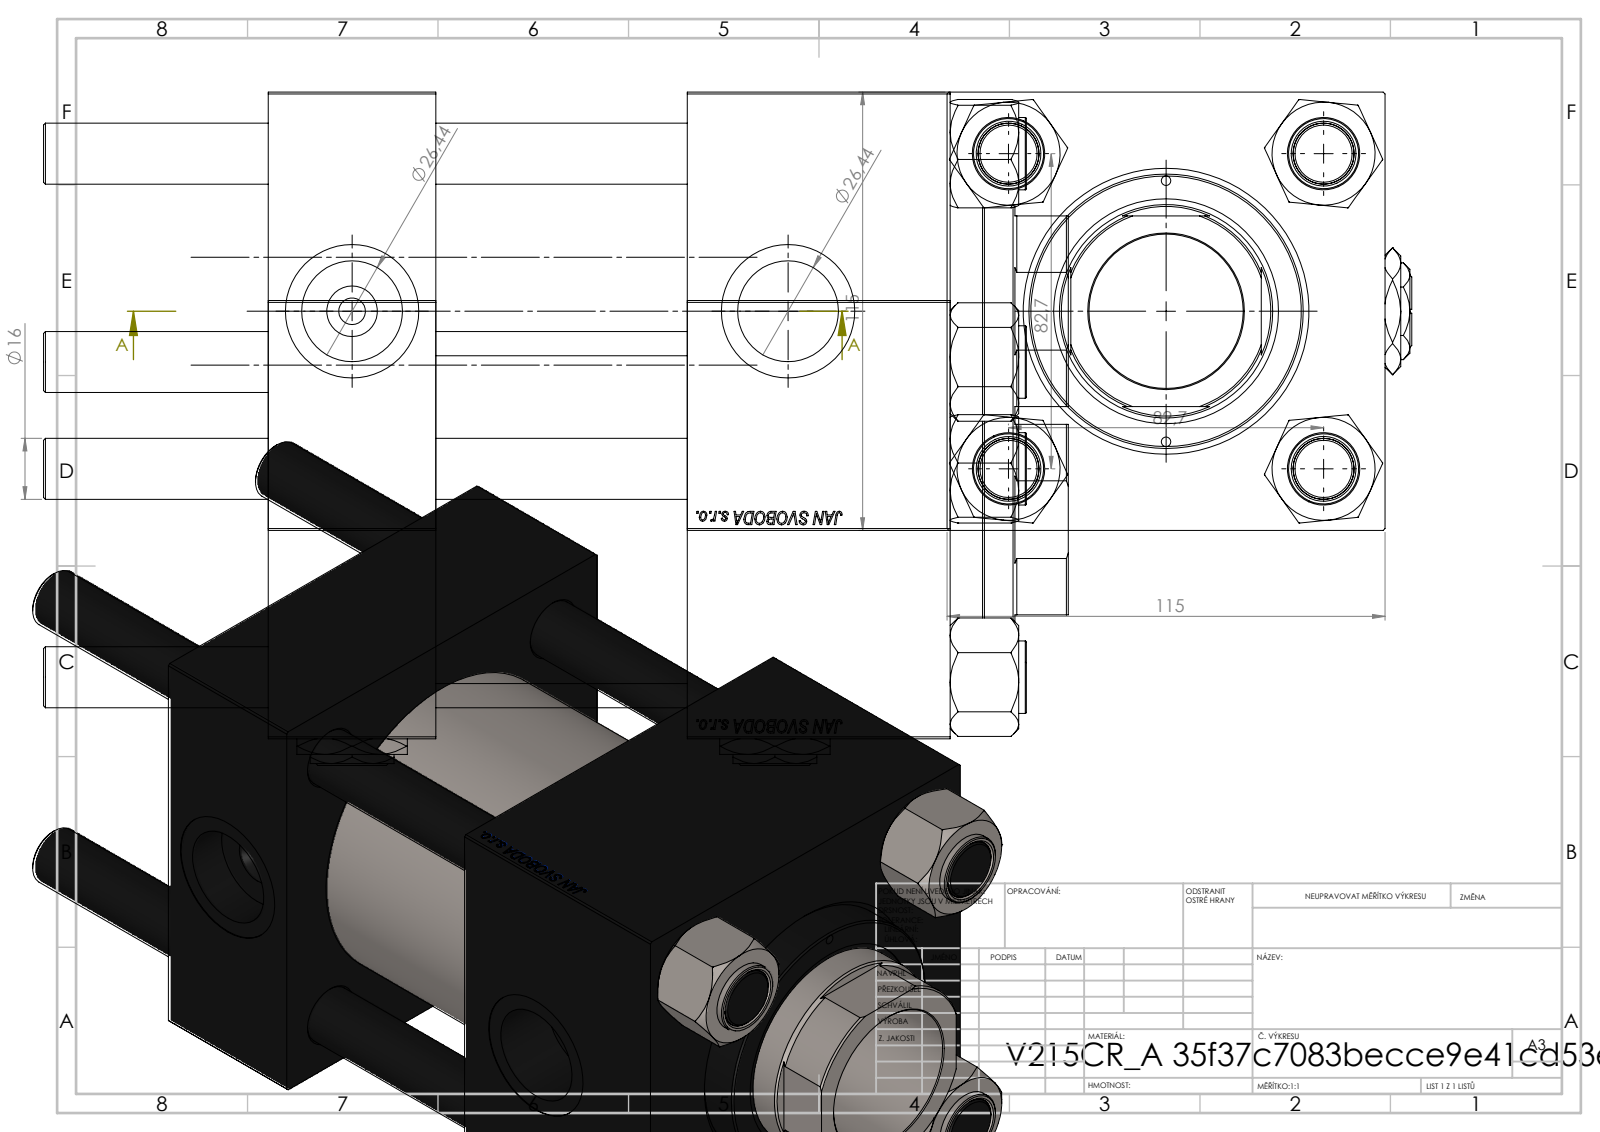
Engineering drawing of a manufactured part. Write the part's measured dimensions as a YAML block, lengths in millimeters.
part_name: "CR025_012_A_0_G_A_G_M_020_+#_##_TYCINKA; V215CR_BODY_A; V215CR_VCP; V215_VC_A (+2 more)"
step_written_by: "SolidWorks 2019 (CONFIG_CONTROL_DESIGN)"
units: millimeters
bodies: {solids: 13, faces: 1285, planar: 615, cylindrical: 92, other: 578}
overall_size: [269, 122, 115]
volume: 1925000
surface_area: 314354
round_holes:
  - {diameter: 16, count: 4}
  - {diameter: 26.44, count: 3}
  - {diameter: 35, count: 3}
  - {diameter: 2.5, count: 2}
  - {diameter: 7, count: 2}
  - {diameter: 23, count: 1}
  - {diameter: 40.5, count: 1}
  - {diameter: 56, count: 1}
  - {diameter: 59, count: 1}
  - {diameter: 61, count: 1}
  - {diameter: 72, count: 1}
  - {diameter: 80, count: 1}
round_bosses_or_shafts:
  - {diameter: 19, count: 4}
  - {diameter: 86, count: 1}
partial_cylinders:
  - {radius: 27, count: 1}
face_to_face_distances: [115, 44, 179, 135, 110, 69, 66, 89, 20, 114.8]
hole_center_spacings: [41.96, 58.48, 82.7, 86.17, 34.25, 116.96, 3.44, 68.5]
